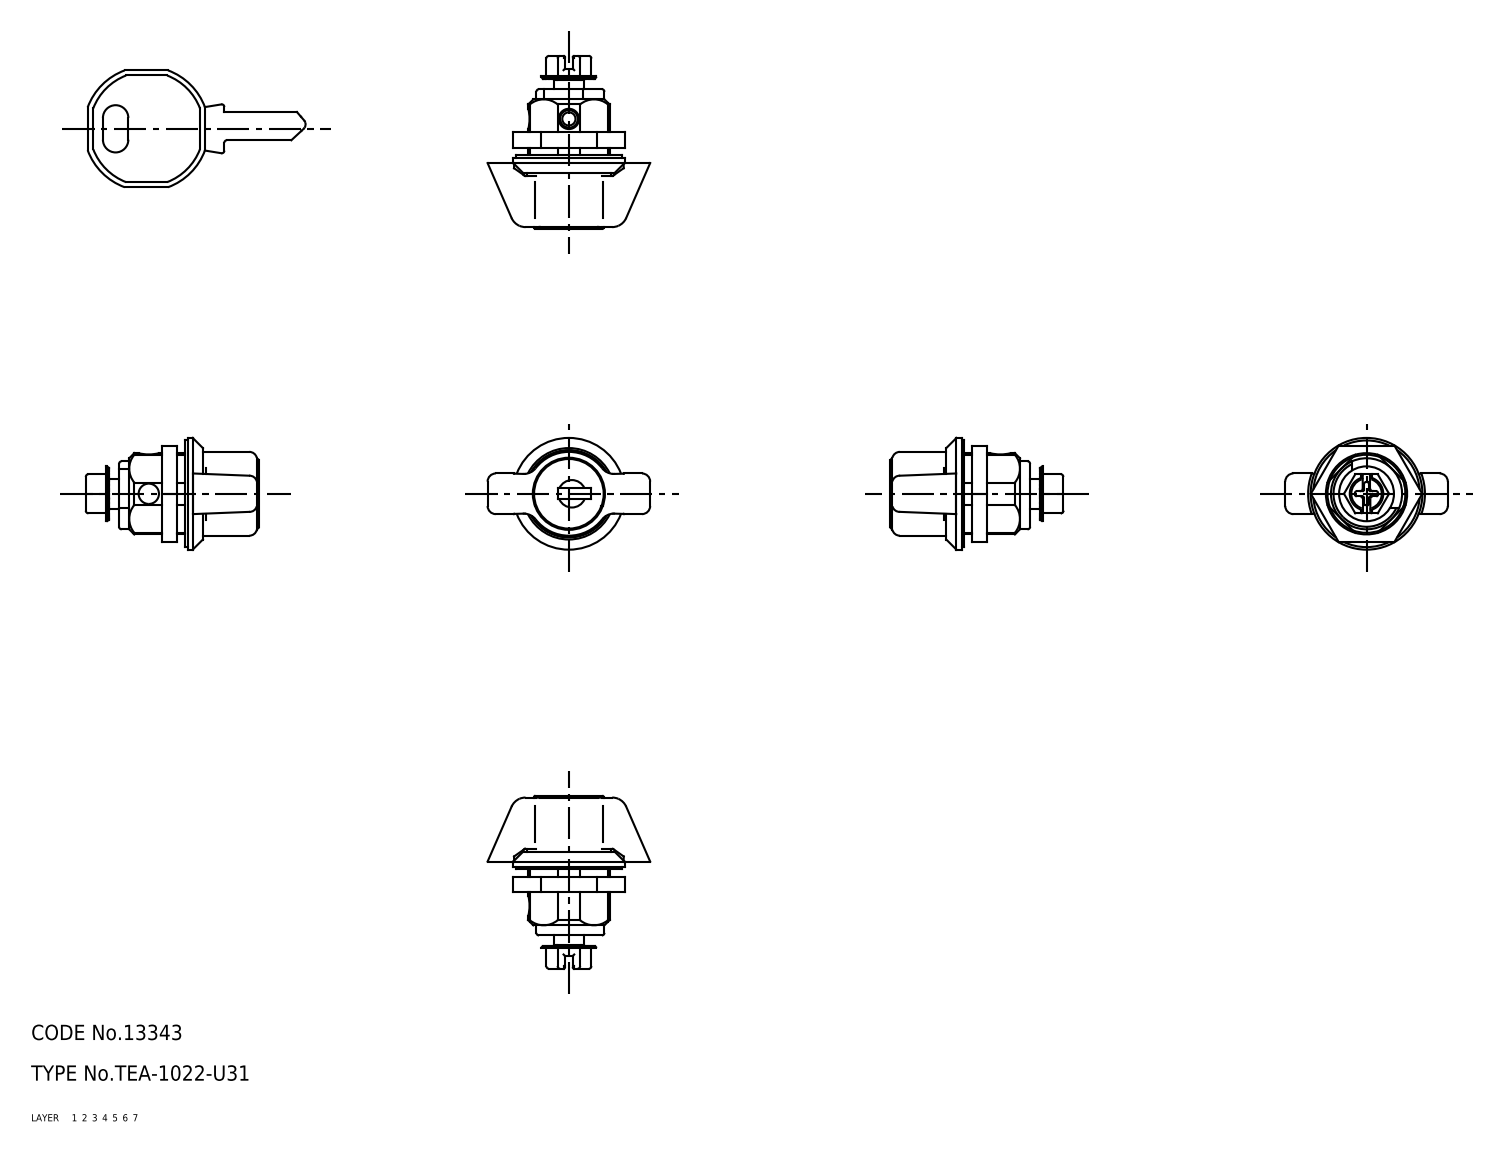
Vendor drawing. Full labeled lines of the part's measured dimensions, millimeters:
Part name (STEP PRODUCT): nut; lock; knob; key (+2 more)
STEP written by: CADfix (AUTOMOTIVE_DESIGN)
Units: millimetres
Bodies: 5 solids, 301 faces (0 planar, 0 cylindrical, 301 other)
Overall size (bounding box): 92.86 × 32 × 22
Volume: 8 913 mm³ · Surface area: 7 828 mm²
